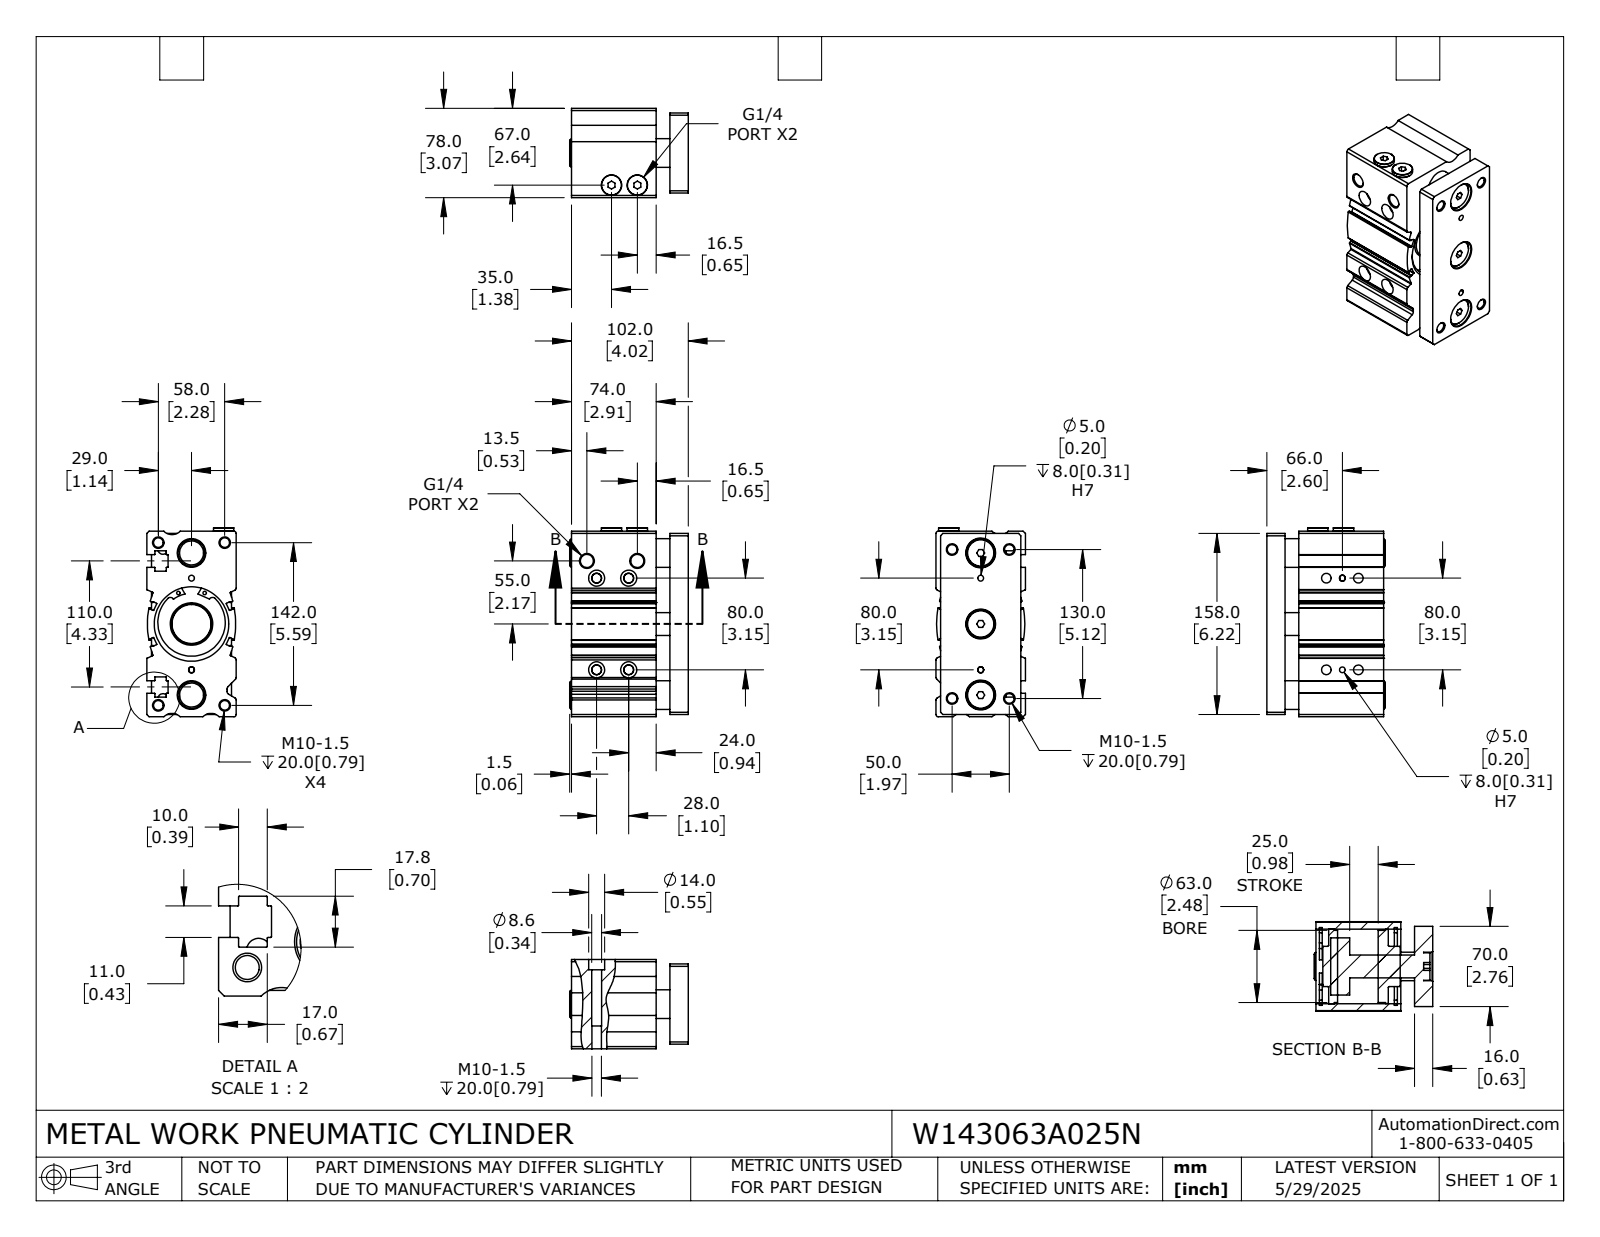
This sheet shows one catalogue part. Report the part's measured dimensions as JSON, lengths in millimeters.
{"part_name": "W143063A025N_BODY; W143063A025N; W143063A025N_ROD", "step_written_by": "SolidWorks 2024 (CONFIG_CONTROL_DESIGN)", "units": "millimeters", "bodies": {"solids": 6, "faces": 454, "planar": 182, "cylindrical": 216, "other": 56}, "overall_size": [165, 103.5, 78], "volume_mm3": 882000, "surface_area_mm2": 183200, "round_holes": [[8.4, 12], [3, 4], [5, 4], [8.6, 4], [14, 4], [25, 3], [11.4, 2], [65, 1]], "round_bosses_or_shafts": [[24, 3], [17.7, 2], [68, 1], [64.8, 1], [63, 1], [50, 1], [35, 1], [20, 1]], "partial_cylinders_radius": [[0.3, 44], [0.5, 12], [2, 8], [2.5, 4], [3, 4], [10, 3], [3.1, 2], [29.4, 2]], "face_to_face_distances": [74, 16, 12, 28, 102, 86, 4, 78, 3, 2.5], "hole_center_spacings": [7.2, 14, 17.3, 25.2, 29.4, 30.4, 35.4, 36.8]}
